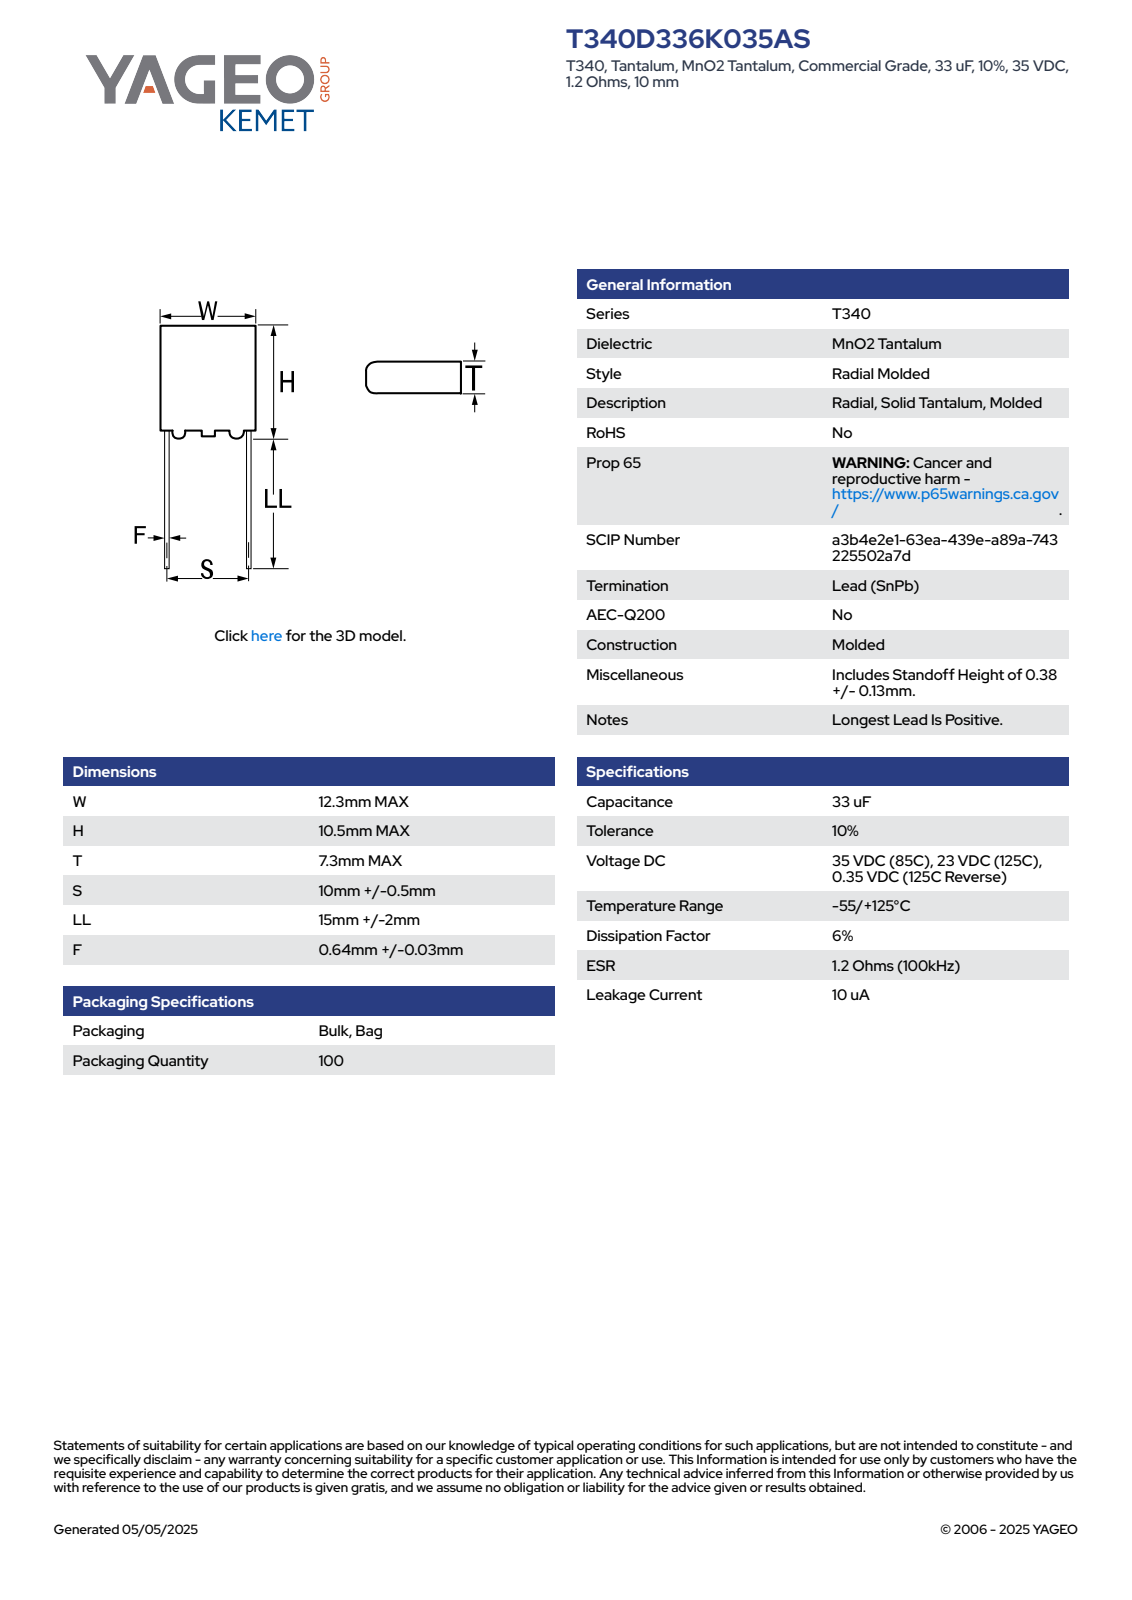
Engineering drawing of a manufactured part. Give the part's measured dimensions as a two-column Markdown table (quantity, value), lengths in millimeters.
| quantity | value |
| --- | --- |
| part name | CTR_T340CDEF_W12.3H10.5T7.3S10LL17F0.67 |
| STEP written by | SolidWorks 2014 (AUTOMOTIVE_DESIGN) |
| units | millimeters |
| bodies | 4 solids, 79 faces (71 planar, 8 cylindrical, 0 other) |
| overall size | 27.5 × 12.3 × 7.3 |
| volume | 916 mm³ |
| surface area | 675 mm² |
| round bosses / shafts (diameter × count) | 0.67 × 2 |
| partial cylindrical surfaces (radius × count) | 0.51 × 2, 1 × 2 |
| main face-to-face distances | 7.3, 9.99, 12.3, 0.51, 10.5, 5.55, 6.75, 1.2, 17, 17.51 |
